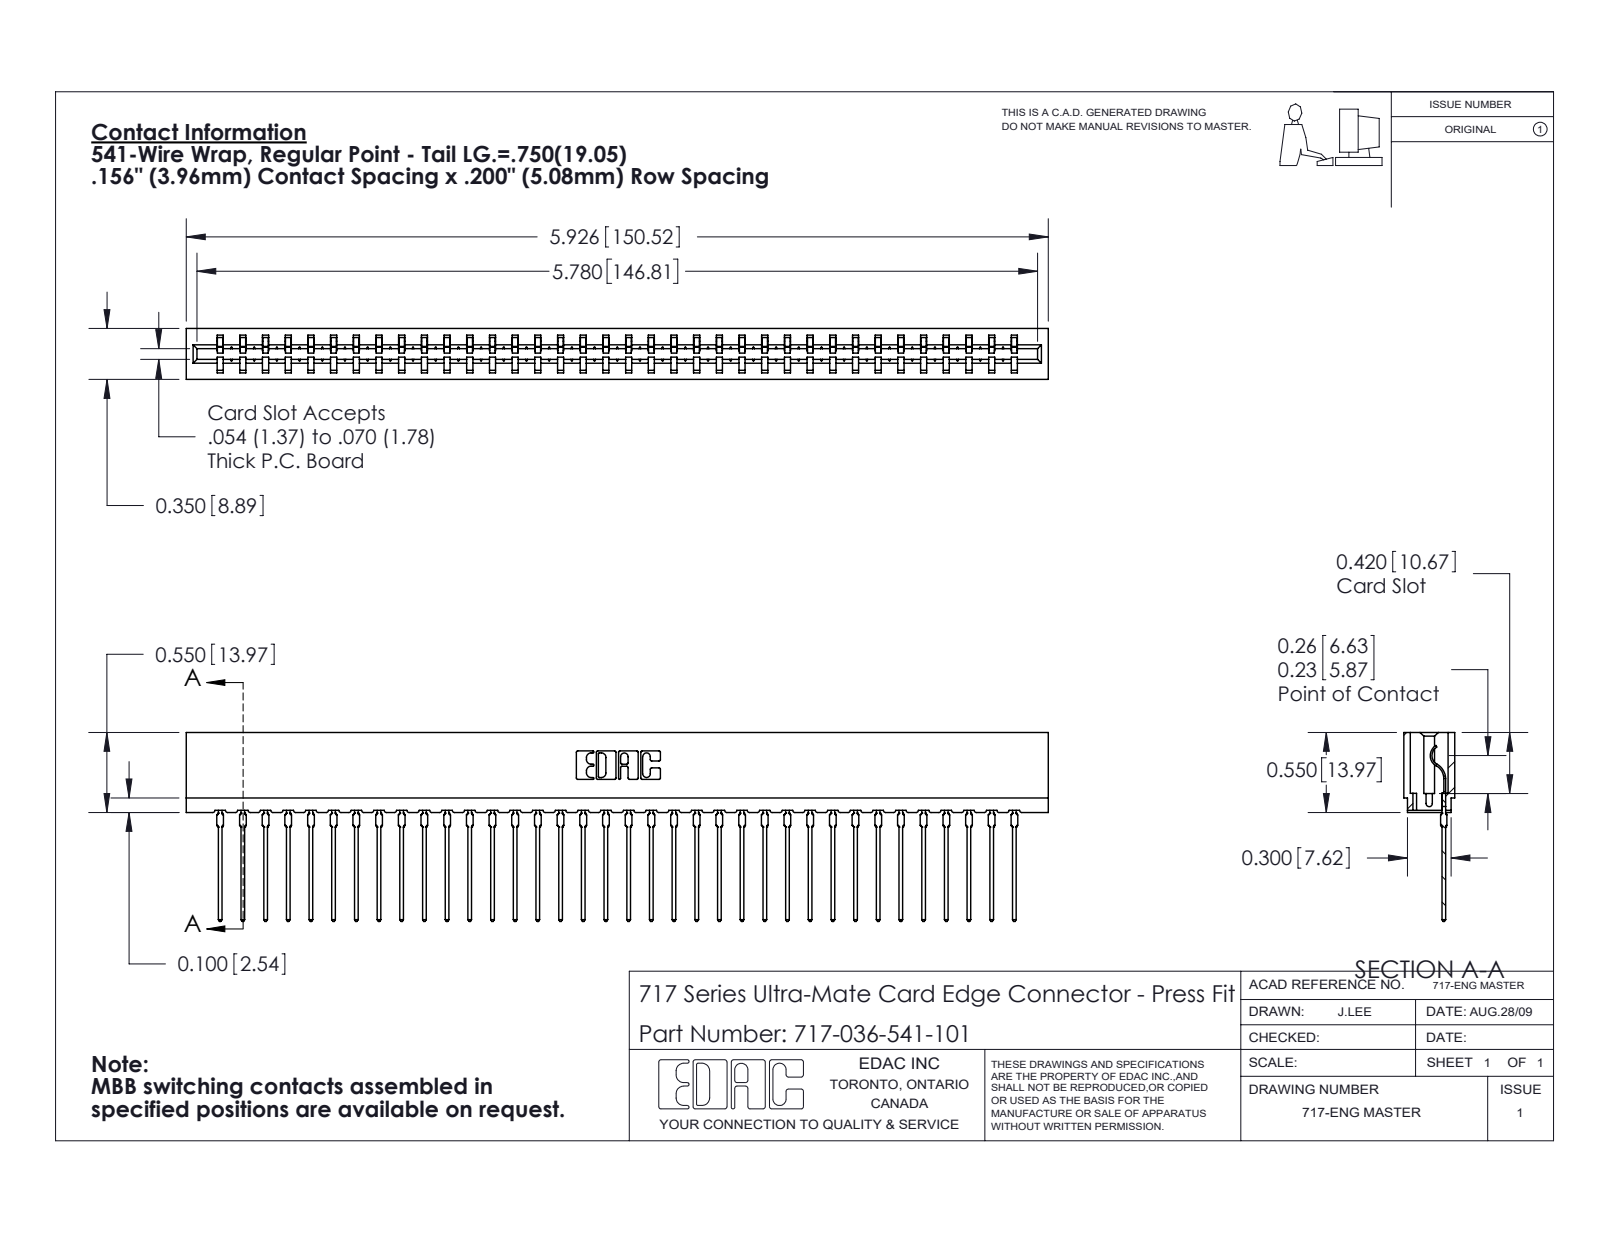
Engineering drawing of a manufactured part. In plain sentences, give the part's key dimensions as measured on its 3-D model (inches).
The part is named "745-292-001_541; 717-036-541-101; 717 Part_Insulator Option - 06". Its 3-D file was written by "SolidWorks 2020 (CONFIG_CONTROL_DESIGN)". It is 37 solids with 4162 faces: 2502 planar, 724 cylindrical and 936 other. Overall it measures 5.926 by 1.299 by 0.35 inches. Its volume is 0.787 cubic inches and its surface area 29.14 square inches. Partial cylindrical surfaces (rounded edges, fillets, slot ends): 72 of radius 0.015, 72 of radius 0.021, 22 of radius 0.01, 6 of radius 0.007, 6 of radius 0.031, 4 of radius 0.005, 4 of radius 0.011, 3 of radius 0.026. The main face-to-face distances are 0.212, 0.138, 0.35, 0.063, 0.287, 0.076, 0.149, 0.074, 0.045, 0.305.
